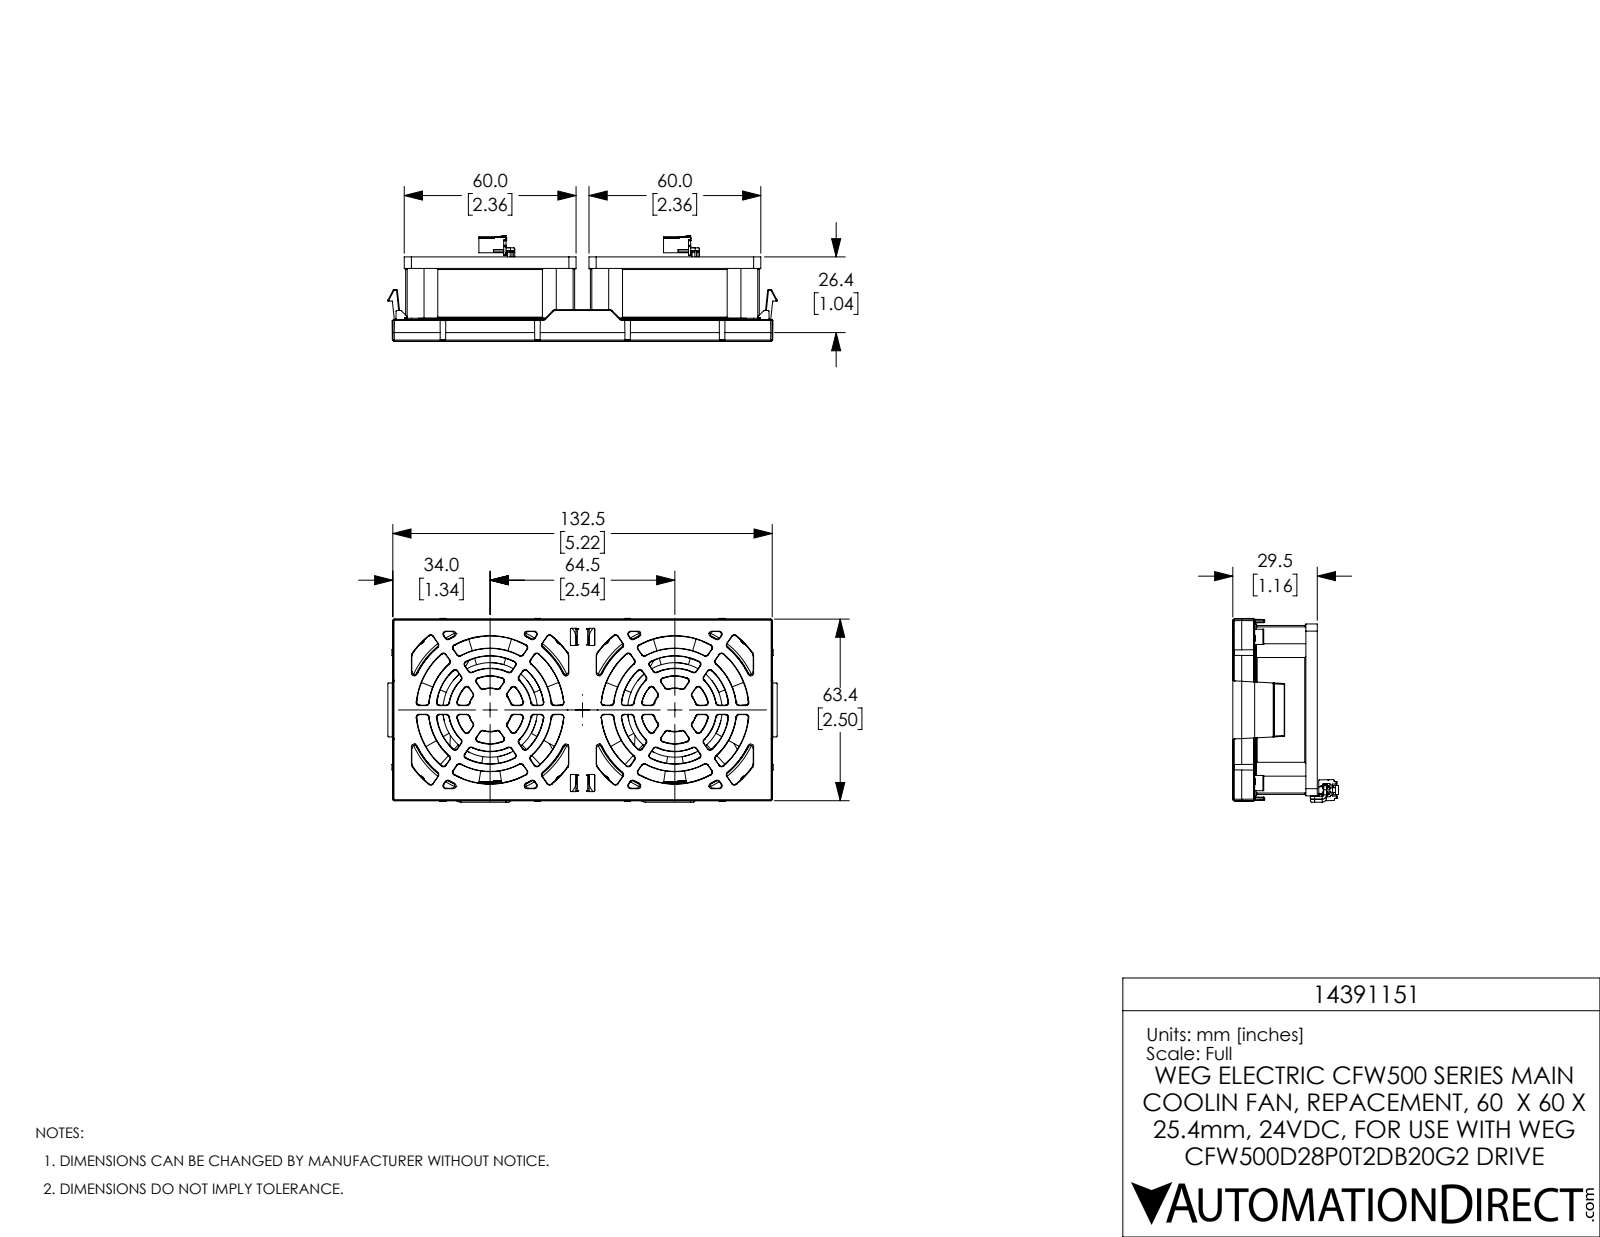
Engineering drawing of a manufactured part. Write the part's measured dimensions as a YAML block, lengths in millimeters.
part_name: "10003688282swa000 R1 NC with ext3 Grill COMPLETE 1"
step_written_by: "SolidWorks 2017 (AUTOMOTIVE_DESIGN)"
units: millimeters
bodies: {solids: 13, faces: 3551, planar: 1182, cylindrical: 671, other: 1698}
overall_size: [135.9, 64.2, 37]
volume: 99830
surface_area: 82580
round_holes:
  - {diameter: 4.3, count: 8}
  - {diameter: 57.5, count: 2}
round_bosses_or_shafts:
  - {diameter: 1, count: 8}
  - {diameter: 59, count: 2}
  - {diameter: 33, count: 2}
partial_cylinders:
  - {radius: 0.3, count: 133}
  - {radius: 0.5, count: 36}
  - {radius: 0.1, count: 16}
  - {radius: 16.5, count: 14}
  - {radius: 28.5, count: 14}
  - {radius: 1, count: 12}
  - {radius: 5, count: 10}
  - {radius: 2.5, count: 8}
face_to_face_distances: [4, 3.5, 0.5, 21.4, 26, 29.5, 4.1, 25.4, 0.6, 2]
hole_center_spacings: [35.4, 50, 64.5, 46.8, 70.7, 81.6, 92.9, 14.5]
